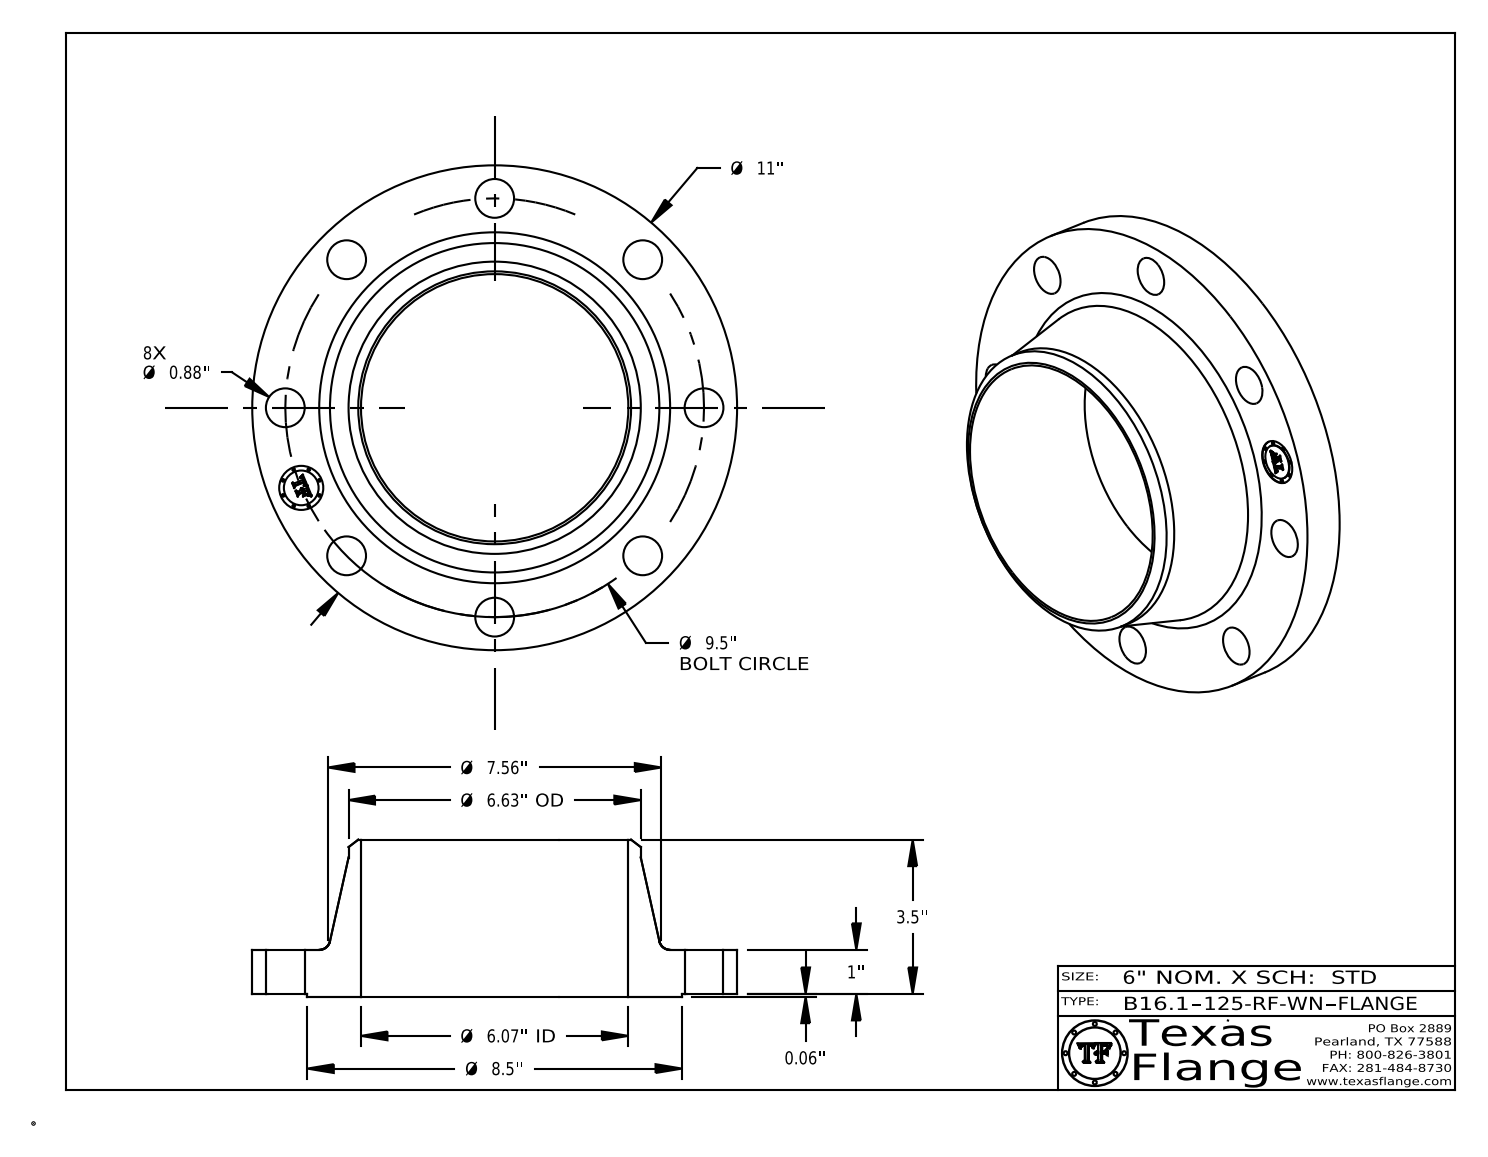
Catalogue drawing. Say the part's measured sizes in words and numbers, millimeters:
The part is named "B16.1, Class 125-RF-WN". Its 3-D file was written by "CATIA V5 STEP AP214 (AUTOMOTIVE_DESIGN)". It is 1 solid with 419 faces: 369 planar, 44 cylindrical and 6 other. Overall it measures 279.4 by 279.4 by 90.5 millimeters. Its volume is 1 435 000 cubic millimeters and its surface area 187 800 square millimeters. Round holes: 8 of diameter 22.4, 1 of diameter 25.4, 1 of diameter 154.1. Round bosses or shafts: 8 of diameter 1.5, 1 of diameter 279.4, 1 of diameter 215.9, 1 of diameter 168.4, 1 of diameter 20. The main face-to-face distances are 25.4, 1.6, 27, 90.5, 88.9, 63.5, 0.4, 26.6, 25, 63.9. The hole center spacings are 120.7, 92.3, 170.6, 222.9, 134.1, 241.3, 241.3, 47.1.
